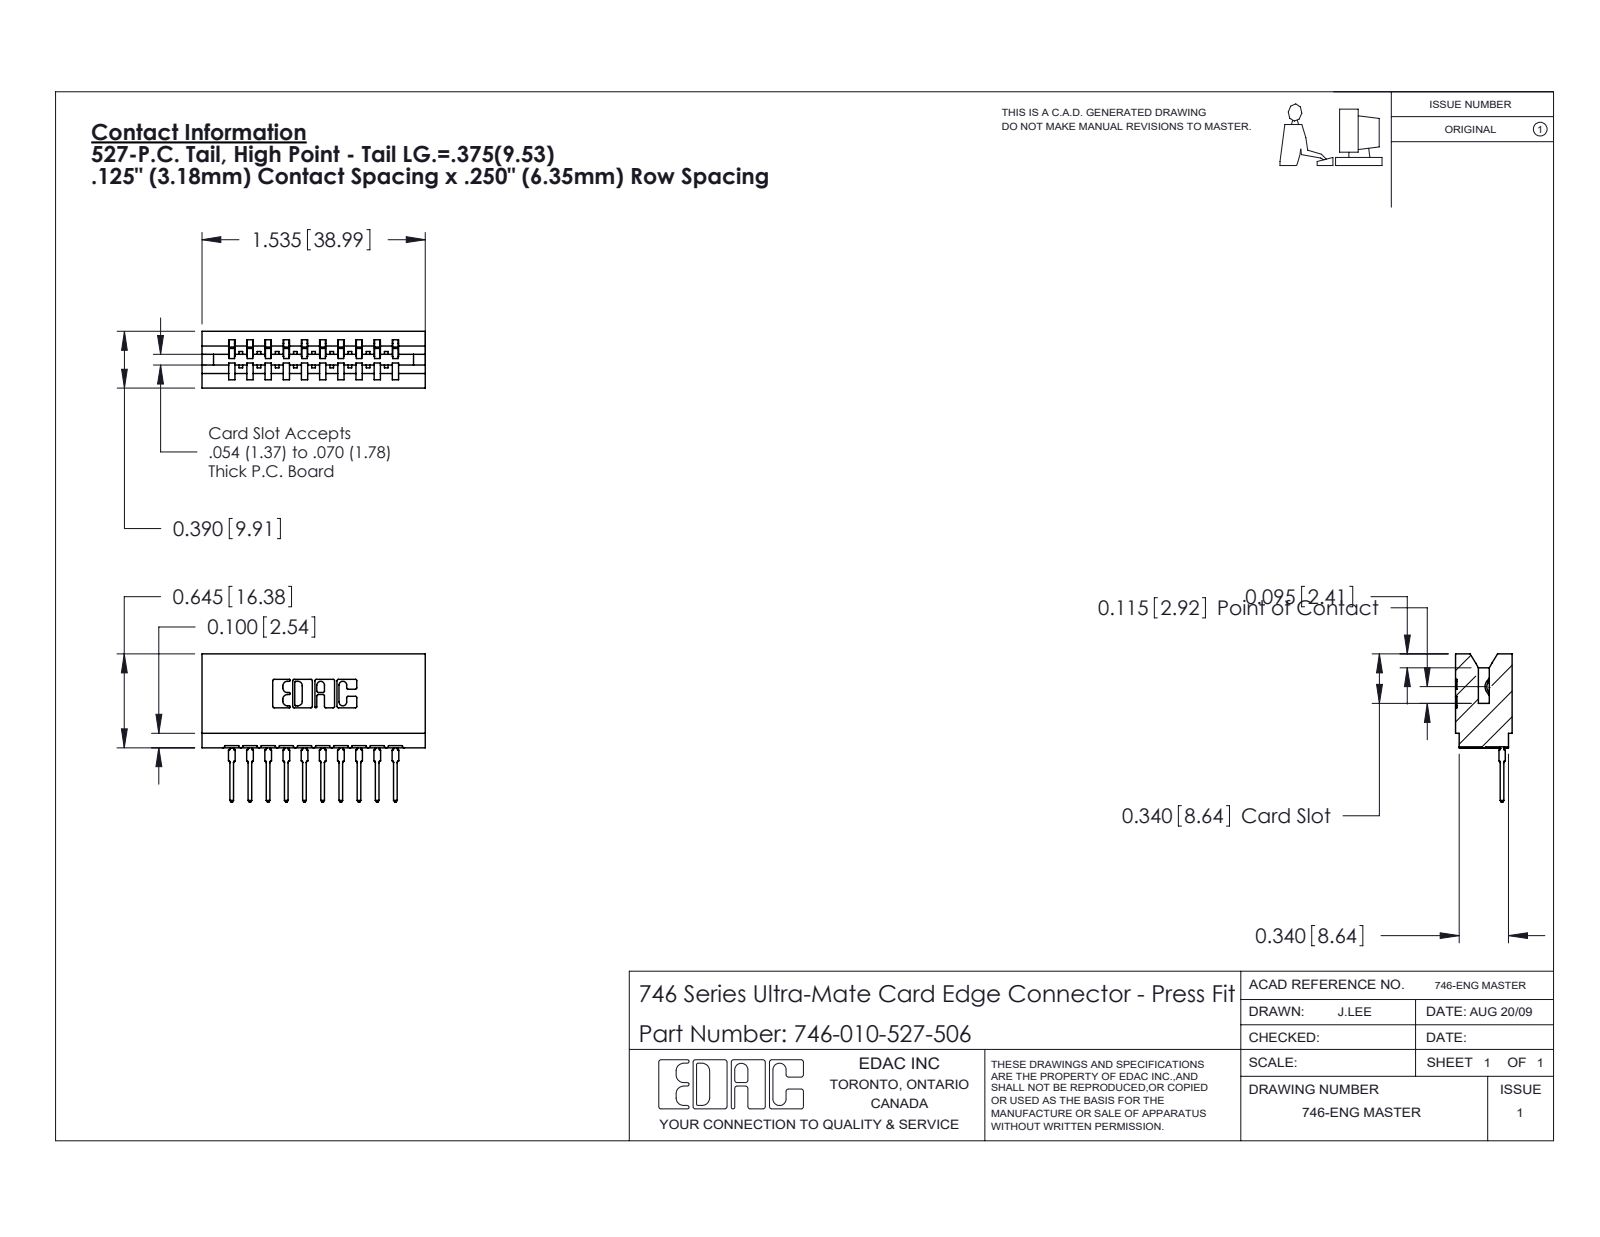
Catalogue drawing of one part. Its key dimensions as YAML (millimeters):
part_name: "746-010-527-506; 746-292-001_527; 746 Part_.340 Slot Depth - 06"
step_written_by: "SolidWorks 2020 (CONFIG_CONTROL_DESIGN)"
units: millimeters
bodies: {solids: 11, faces: 1178, planar: 686, cylindrical: 232, other: 260}
overall_size: [39, 25.9, 9.9]
volume: 4560
surface_area: 5729
partial_cylinders:
  - {radius: 0.3, count: 22}
  - {radius: 0.5, count: 20}
  - {radius: 0.4, count: 11}
  - {radius: 0.2, count: 6}
  - {radius: 0.8, count: 6}
  - {radius: 0.1, count: 4}
  - {radius: 0.3, count: 4}
  - {radius: 0.7, count: 3}
face_to_face_distances: [6.4, 12.7, 8.5, 1.1, 3.2, 1.4, 19.1, 3.2, 9.9, 7.4]
